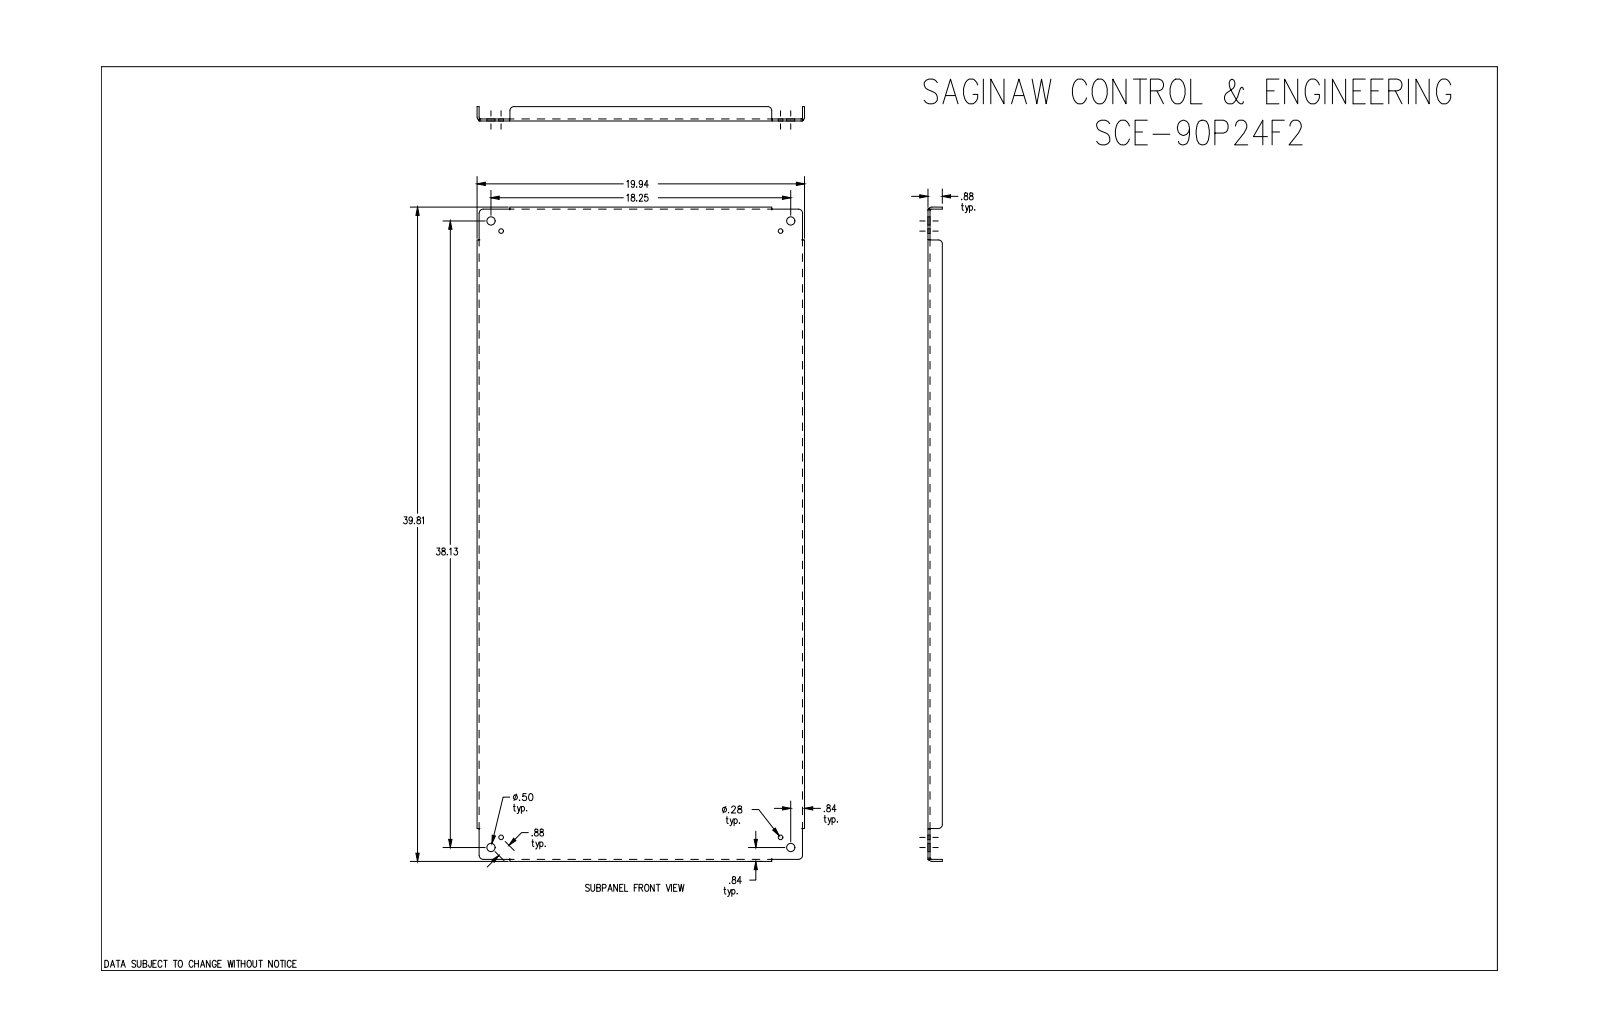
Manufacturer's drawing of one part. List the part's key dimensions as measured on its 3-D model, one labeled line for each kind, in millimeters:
Part name (STEP PRODUCT): SCE-90P24F2
STEP written by: SolidWorks 2019 (AUTOMOTIVE_DESIGN)
Units: millimetres
Bodies: 1 solid, 82 faces (30 planar, 28 cylindrical, 24 other)
Overall size (bounding box): 1011.3 × 506.4 × 22.2
Volume: 1 763 000 mm³ · Surface area: 1 121 000 mm²
Round holes (diameter × count): ⌀7.1 ×4, ⌀12.7 ×4
Partial cylindrical surfaces — rounded edges, fillets, slot ends (radius × count): R6.4 ×8, R2.8 ×4, R6 ×4
Main face-to-face distances: 3.2, 3.2, 503.3, 500, 506.4, 1008, 19.1, 22.2, 1004.9, 1011.3
Hole centre spacings: 22.2, 448.1, 952.8, 1052.7, 432.1, 463.6, 936.9, 968.4
